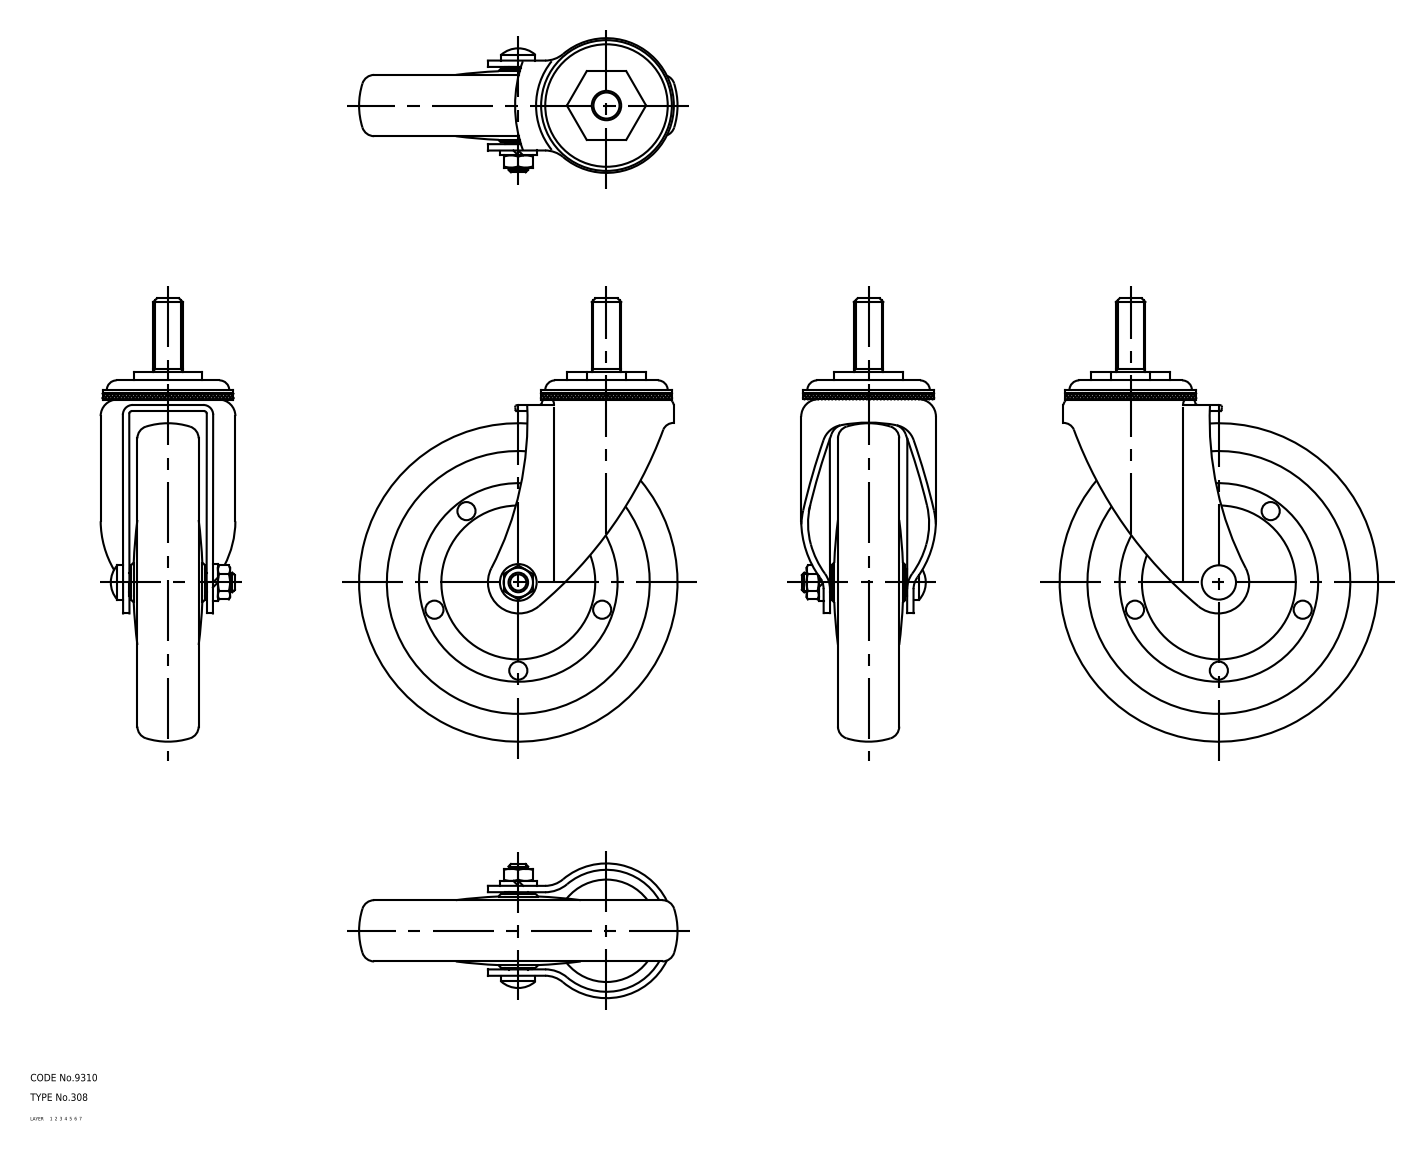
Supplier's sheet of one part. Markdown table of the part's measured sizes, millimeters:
| quantity | value |
| --- | --- |
| part name | wheel; axle; main shaft; No_308_24782_36 |
| STEP written by | CADfix (AUTOMOTIVE_DESIGN) |
| units | millimeters |
| bodies | 4 solids, 188 faces (0 planar, 0 cylindrical, 188 other) |
| overall size | 181 × 130 × 55 |
| volume | 305 661 mm³ |
| surface area | 69 367 mm² |
